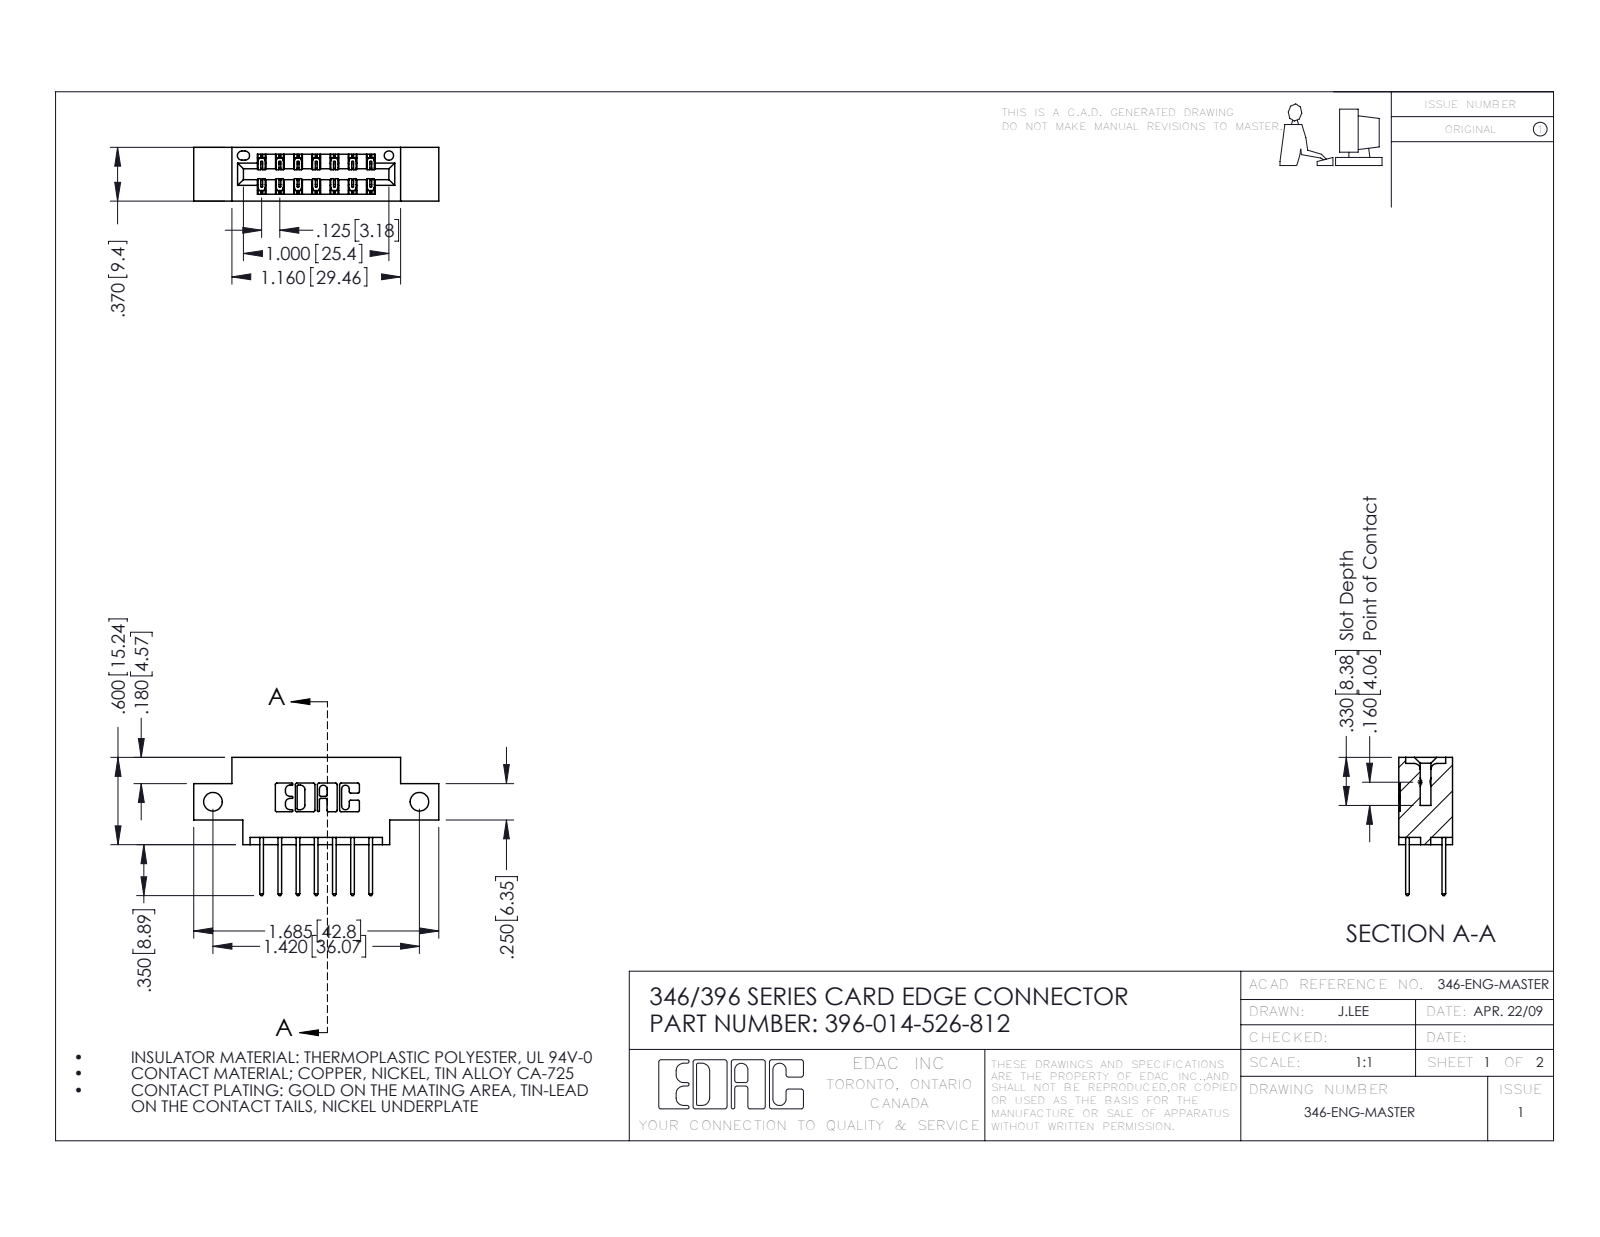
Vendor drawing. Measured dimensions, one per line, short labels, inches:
name: 345-292-001_345-293-126; 396-014-526-812; 346 Part_0.170 Offset - Side Mount
written by: SolidWorks 2016 (CONFIG_CONTROL_DESIGN)
unit: in
bodies: 15 solids, 854 faces (570 planar, 284 cylindrical, 0 other)
size: 1.685 × 0.95 × 0.37
volume: 0.225 in³; area: 7.218 in²
holes: 2× ⌀0.128, 1× ⌀0.064
rounds: 22× R0.01, 21× R0.006, 14× R0.01, 6× R0.007, 6× R0.031, 3× R0.026, 2× R0.014, 2× R0.022
face distances: 0.25, 0.37, 0.048, 0.322, 0.072, 0.298, 0.025, 0.275, 0.148, 0.222
hole spacings: 1.42
